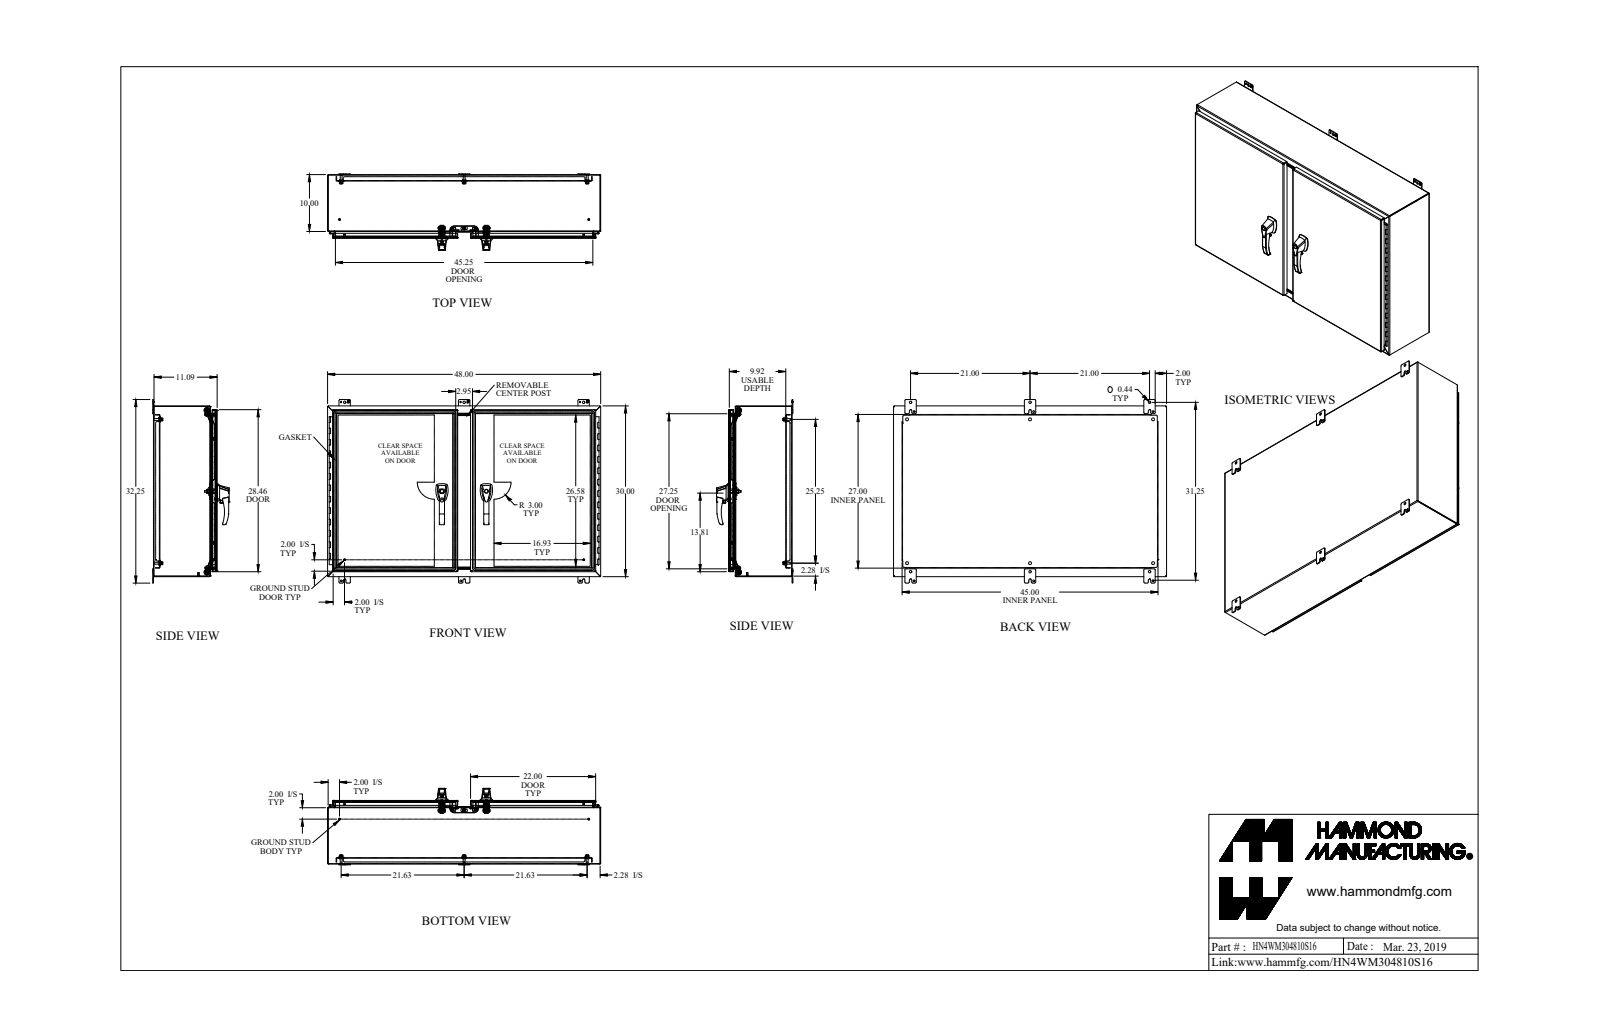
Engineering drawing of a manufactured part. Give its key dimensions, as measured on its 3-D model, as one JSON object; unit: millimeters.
{"part_name": "HN4WM304810S16", "step_written_by": "SolidWorks 2018 (AUTOMOTIVE_DESIGN)", "units": "millimeters", "bodies": {"solids": 106, "faces": 2796, "planar": 1313, "cylindrical": 1203, "other": 280}, "overall_size": [1219.2, 819.2, 341], "volume_mm3": 10860000, "surface_area_mm2": 8909000, "round_holes": [[7.7, 10], [8, 9], [6.4, 8], [5.1, 6], [7.8, 6], [11.3, 6], [12.7, 6], [7.1, 4], [8, 4], [9.9, 4], [11.1, 3], [2.8, 2]], "round_bosses_or_shafts": [[25.4, 8], [16.5, 6], [9.5, 6], [8.4, 6], [7.4, 6], [19.1, 4], [15.9, 4], [11.2, 4]], "partial_cylinders_radius": [[3.2, 37], [6.4, 34], [0.5, 32], [4.8, 26], [1.5, 22], [12.7, 22], [1.2, 19], [3.6, 19]], "face_to_face_distances": [2.4, 26.2, 2.4, 281.7, 279.3, 284.1, 281.7, 253.1, 28.6, 255.5], "hole_center_spacings": [549.3, 152.4, 1181.3, 844.4, 304.8, 549.3, 641.4, 844.4]}
